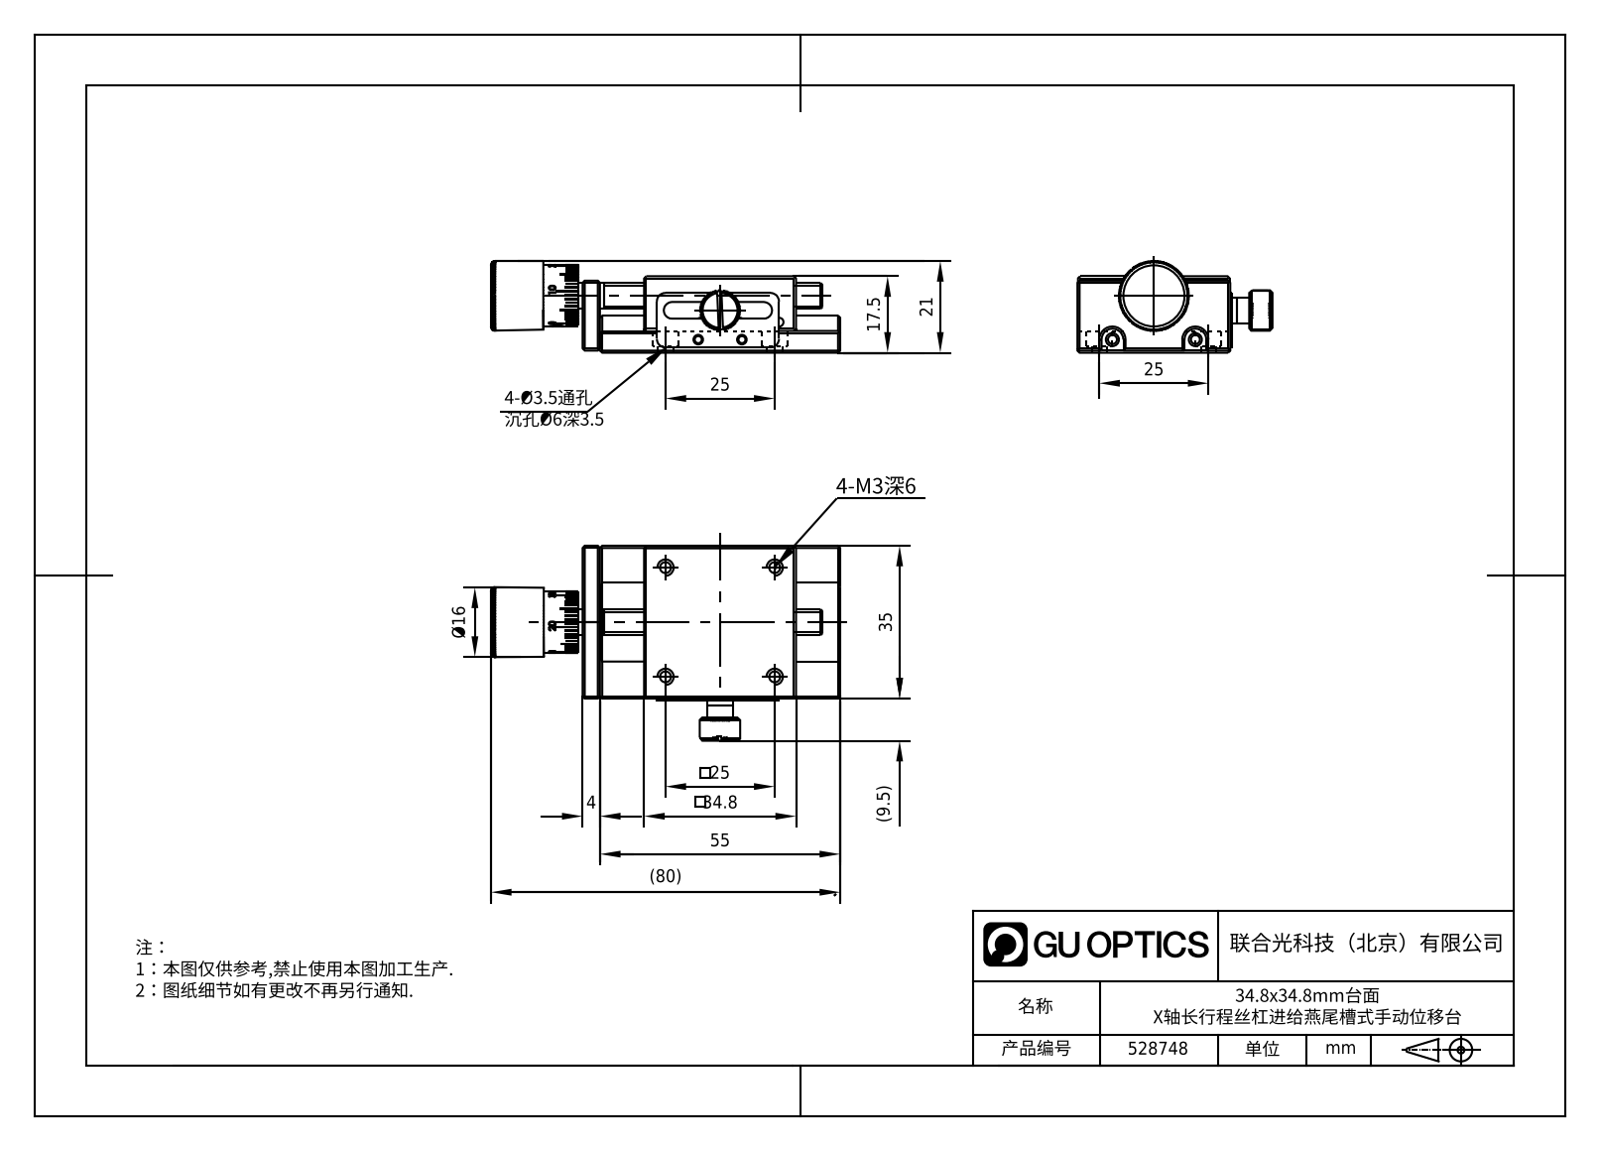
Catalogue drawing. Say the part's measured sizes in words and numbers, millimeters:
The part is named "528748". Its 3-D file was written by "SolidWorks 2020 (CONFIG_CONTROL_DESIGN)". It is 16 solids with 494 faces: 308 planar, 95 cylindrical and 91 other. Overall it measures 79 by 42.14 by 20.5 millimeters. Its volume is 30 779 cubic millimeters and its surface area 18 726 square millimeters. Round holes: 6 of diameter 1.6, 6 of diameter 2.5, 5 of diameter 2.05, 5 of diameter 6, 4 of diameter 3.4, 3 of diameter 3, 2 of diameter 1.5, 2 of diameter 2.2, 1 of diameter 3.5, 1 of diameter 4.1, 1 of diameter 5, 1 of diameter 7. Round bosses or shafts: 3 of diameter 4.5, 3 of diameter 4, 3 of diameter 2, 2 of diameter 2.5, 1 of diameter 15, 1 of diameter 13, 1 of diameter 8.5, 1 of diameter 7. Partial cylindrical surfaces (rounded edges, fillets, slot ends): 8 of radius 0.3, 4 of radius 0.5, 4 of radius 2, 2 of radius 1.4, 2 of radius 2.5. The main face-to-face distances are 5, 3.5, 12.5, 8.5, 17.5, 9, 34.8, 3.8, 8.7, 0.5. The hole center spacings are 25, 0.67, 35.36, 9, 3, 5.25, 10, 13.77.
